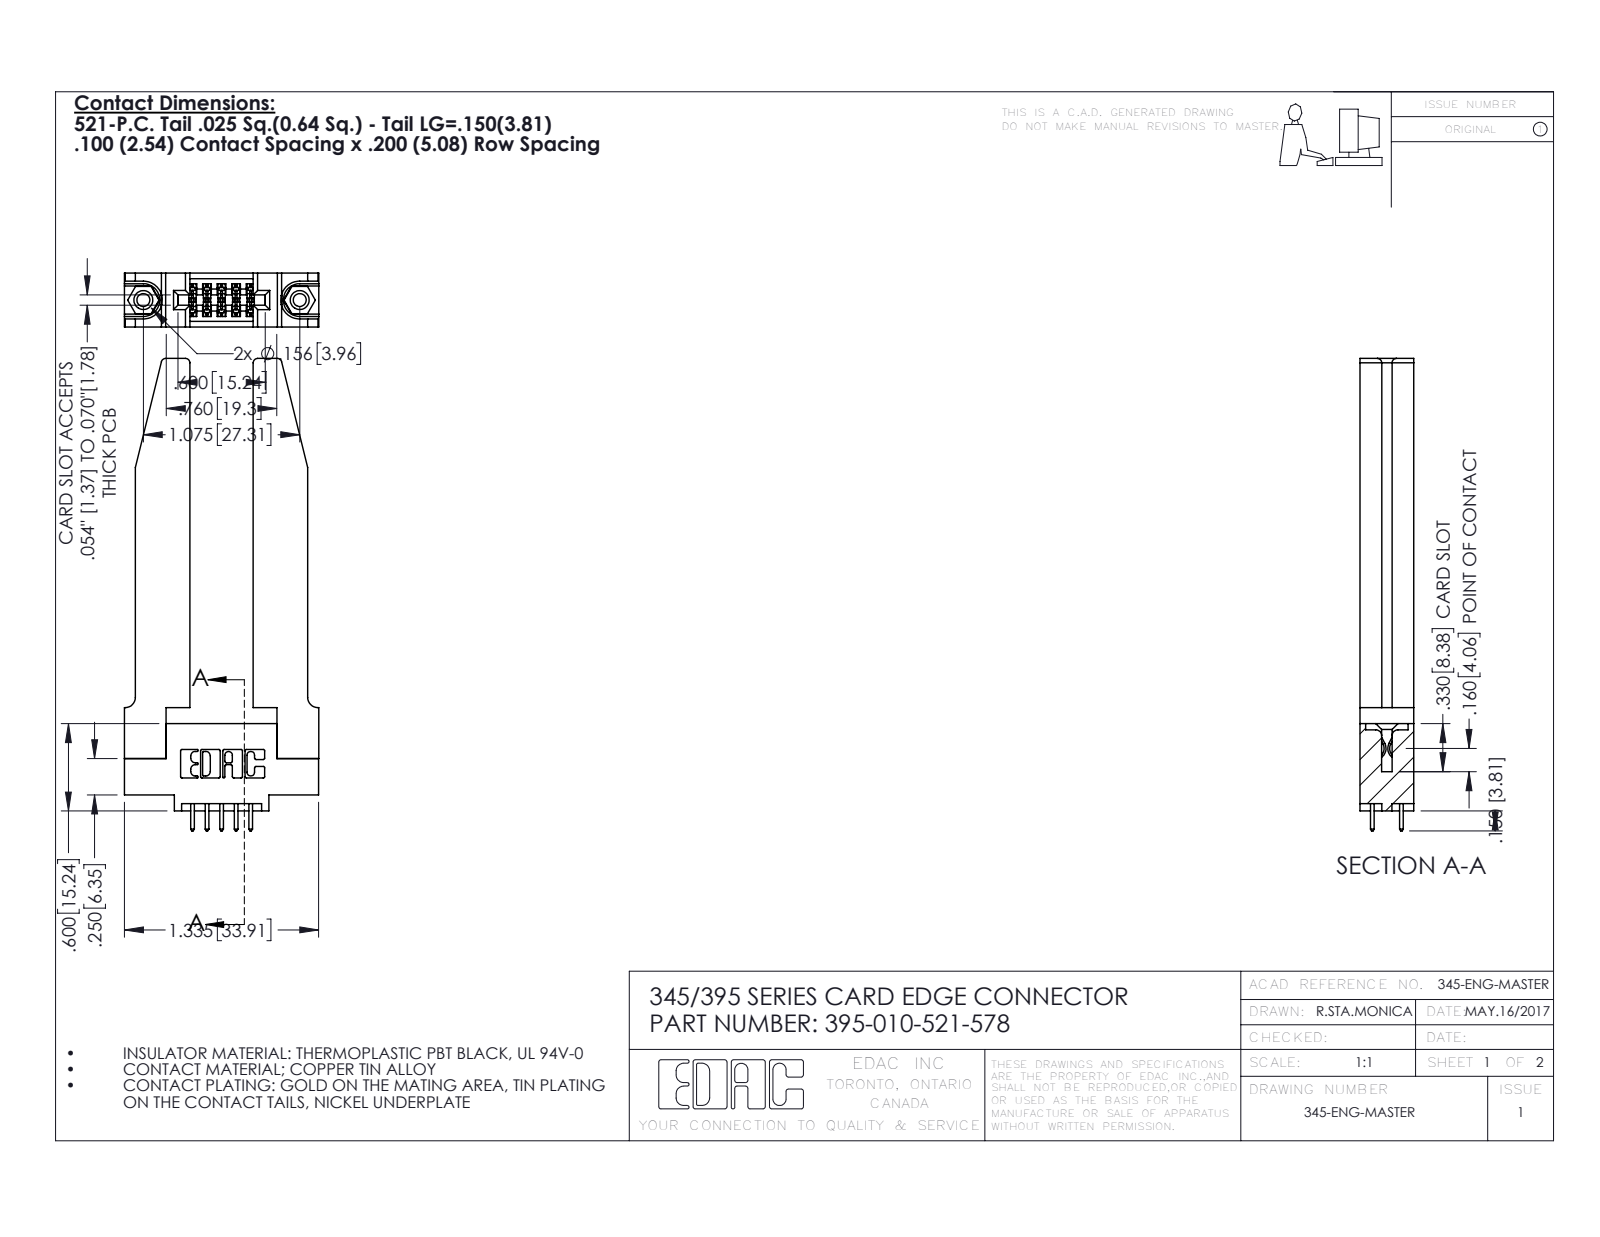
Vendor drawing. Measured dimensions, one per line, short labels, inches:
name: 345-250-001_345-250-001-102; 395-010-521-578; 345-292-001_345-293-121; 345-220-078_345-220-078 (+1 more)
written by: SolidWorks 2016 (CONFIG_CONTROL_DESIGN)
unit: in
bodies: 15 solids, 864 faces (556 planar, 256 cylindrical, 52 other)
size: 3.247 × 1.336 × 0.37
volume: 0.65 in³; area: 16.18 in²
holes: 2× ⌀0.089, 2× ⌀0.125, 2× ⌀0.156, 1× ⌀0.064
bosses: 2× ⌀0.155
rounds: 22× R0.01, 15× R0.006, 10× R0.01, 8× R0.03, 6× R0.007, 6× R0.031, 3× R0.026, 2× R0.014
face distances: 0.37, 0.15, 0.22, 0.435, 0.148, 0.072, 0.298, 0.077, 0.2, 0.071
hole spacings: 0.27, 0.847, 1.075
